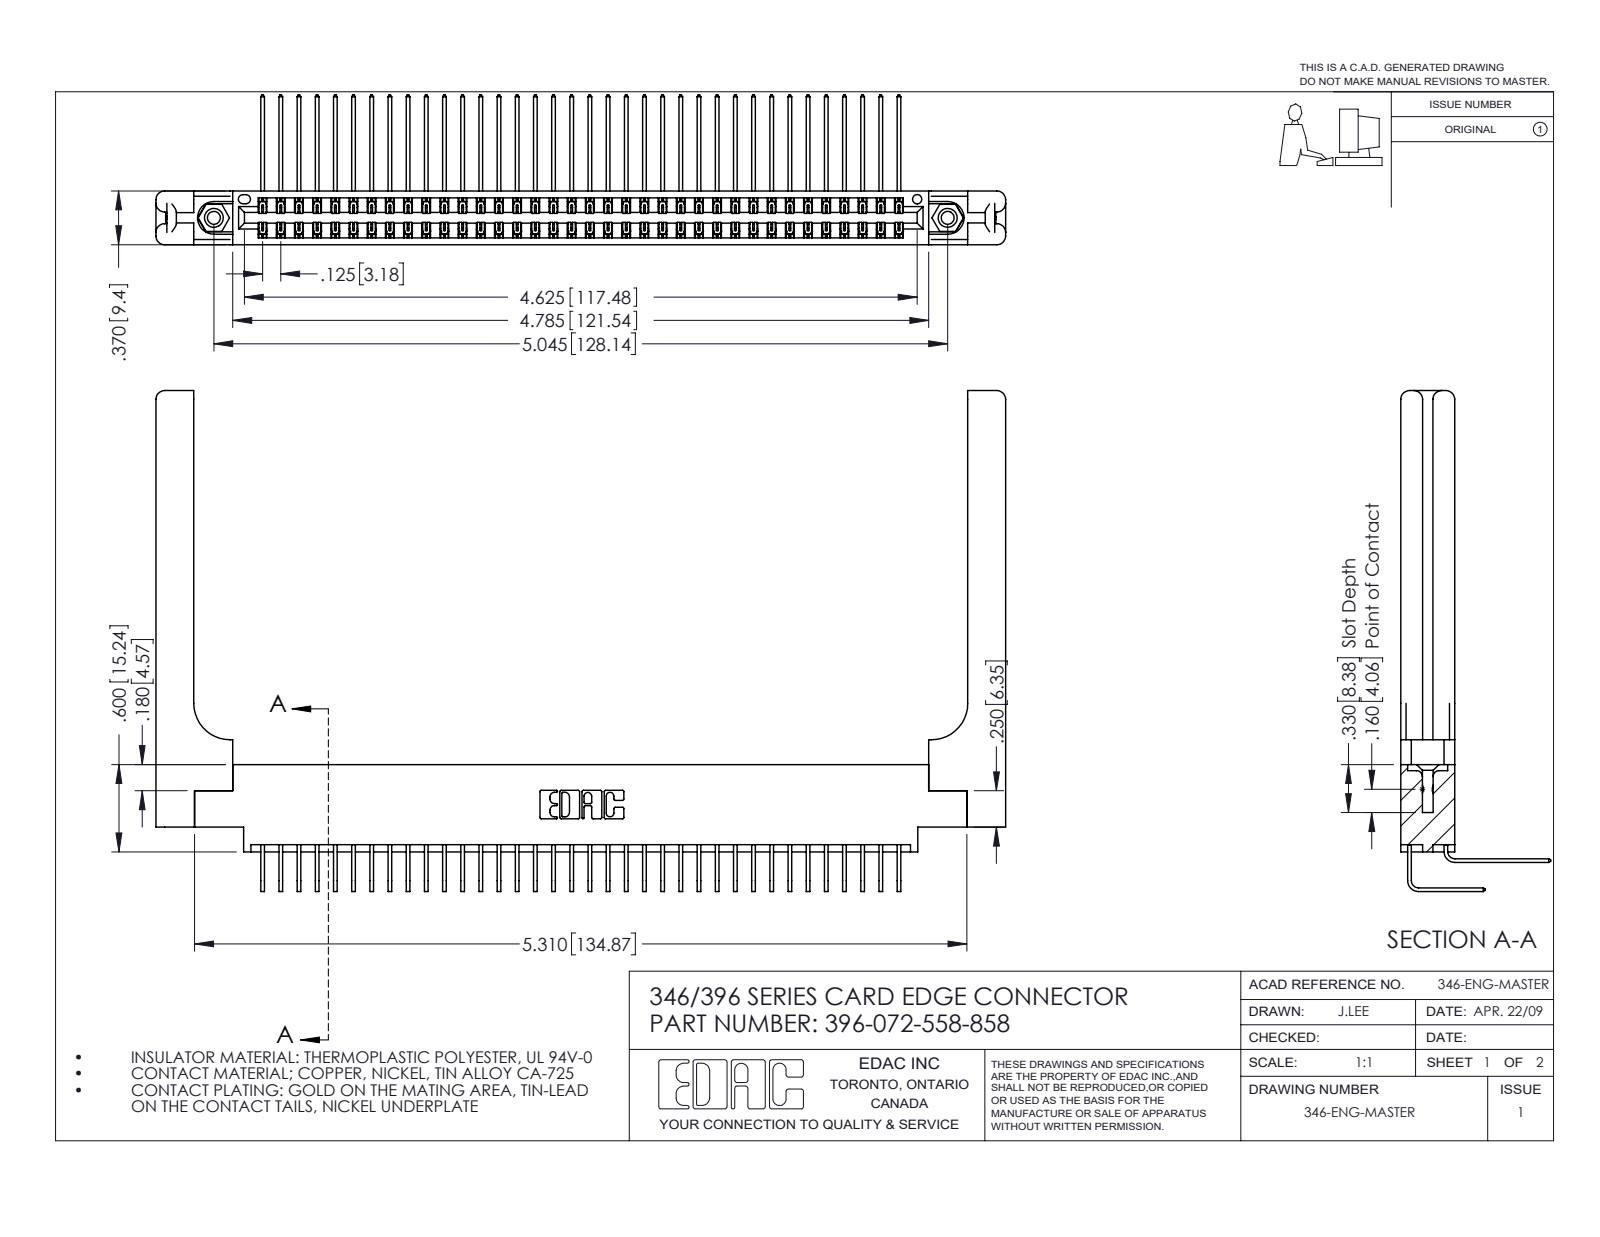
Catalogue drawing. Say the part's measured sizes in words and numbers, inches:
The part is named "345-250-001_345-250-001-102; 345-292-001_558 Tail - 2; 346 Part_0.170 Offset - 0.156 Dia-TH; 396-072-558-858 (+2 more)". Its 3-D file was written by "SolidWorks 2016 (CONFIG_CONTROL_DESIGN)". It is 77 solids with 4270 faces: 2892 planar, 1318 cylindrical and 60 other. Overall it measures 5.841 by 3.443 by 1.03 inches. Its volume is 1.353 cubic inches and its surface area 42.21 square inches. Round holes: 2 of diameter 0.089, 2 of diameter 0.125, 2 of diameter 0.156, 1 of diameter 0.064. Round bosses or shafts: 2 of diameter 0.155. Partial cylindrical surfaces (rounded edges, fillets, slot ends): 108 of radius 0.006, 22 of radius 0.01, 16 of radius 0.06, 6 of radius 0.007, 6 of radius 0.031, 3 of radius 0.026, 2 of radius 0.014, 2 of radius 0.022. The main face-to-face distances are 0.37, 0.322, 0.048, 0.072, 0.025, 0.148, 0.15, 0.298, 0.25, 0.275. The hole center spacings are 0.246, 4.836, 5.045.
